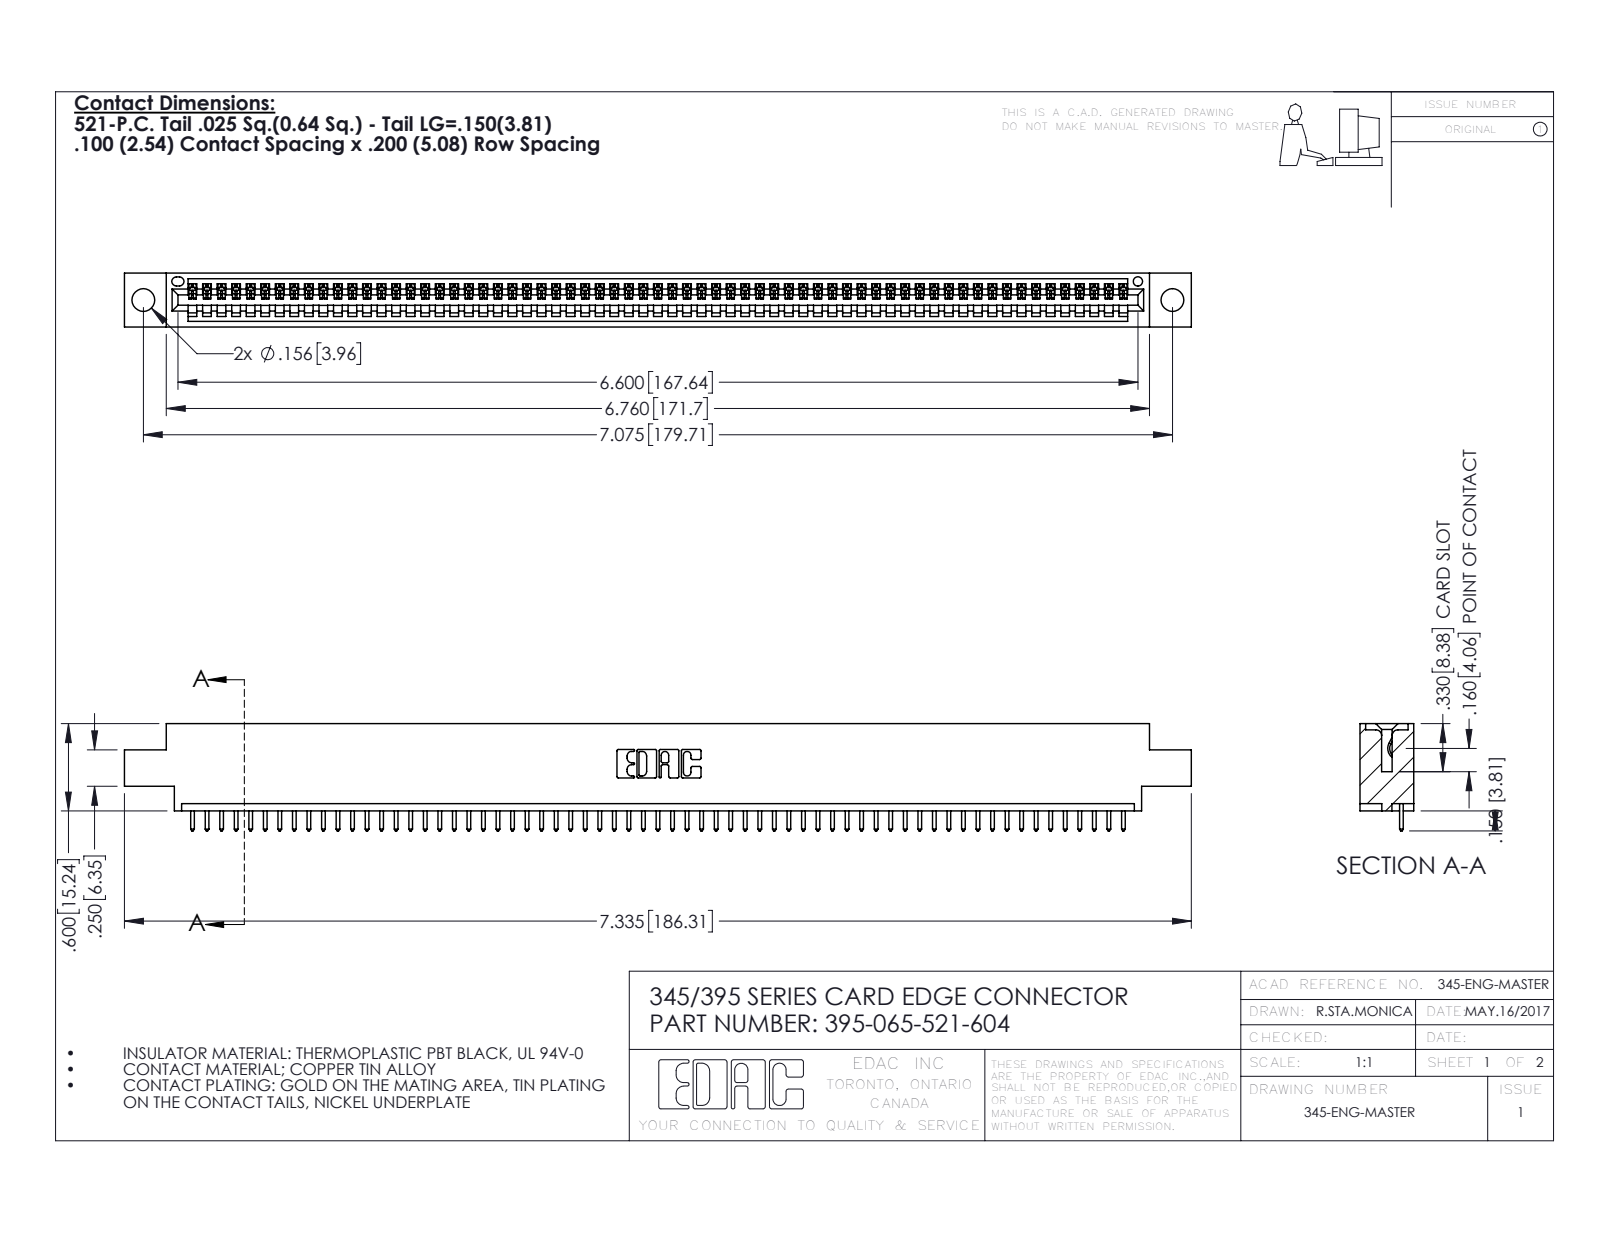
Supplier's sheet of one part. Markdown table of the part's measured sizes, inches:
| quantity | value |
| --- | --- |
| part name | 345-292-001_345-293-121; 395-065-521-604; 345 Part_0.170 Offset - 0.156 Dia-TH |
| STEP written by | SolidWorks 2016 (CONFIG_CONTROL_DESIGN) |
| units | inches |
| bodies | 66 solids, 3900 faces (2684 planar, 1216 cylindrical, 0 other) |
| overall size | 7.335 × 0.737 × 0.37 |
| volume | 1.068 in³ |
| surface area | 35.31 in² |
| round holes (diameter × count) | 0.156 × 2, 0.064 × 1 |
| partial cylindrical surfaces (radius × count) | 0.006 × 130, 0.01 × 130, 0.01 × 22, 0.007 × 6, 0.031 × 6, 0.026 × 3, 0.031 × 2, 0.04 × 2 |
| main face-to-face distances | 0.298, 0.072, 0.37, 0.2, 0.098, 0.272, 0.025, 0.225, 0.175, 0.149 |
| hole center spacings | 0.27, 6.839, 7.075 |
